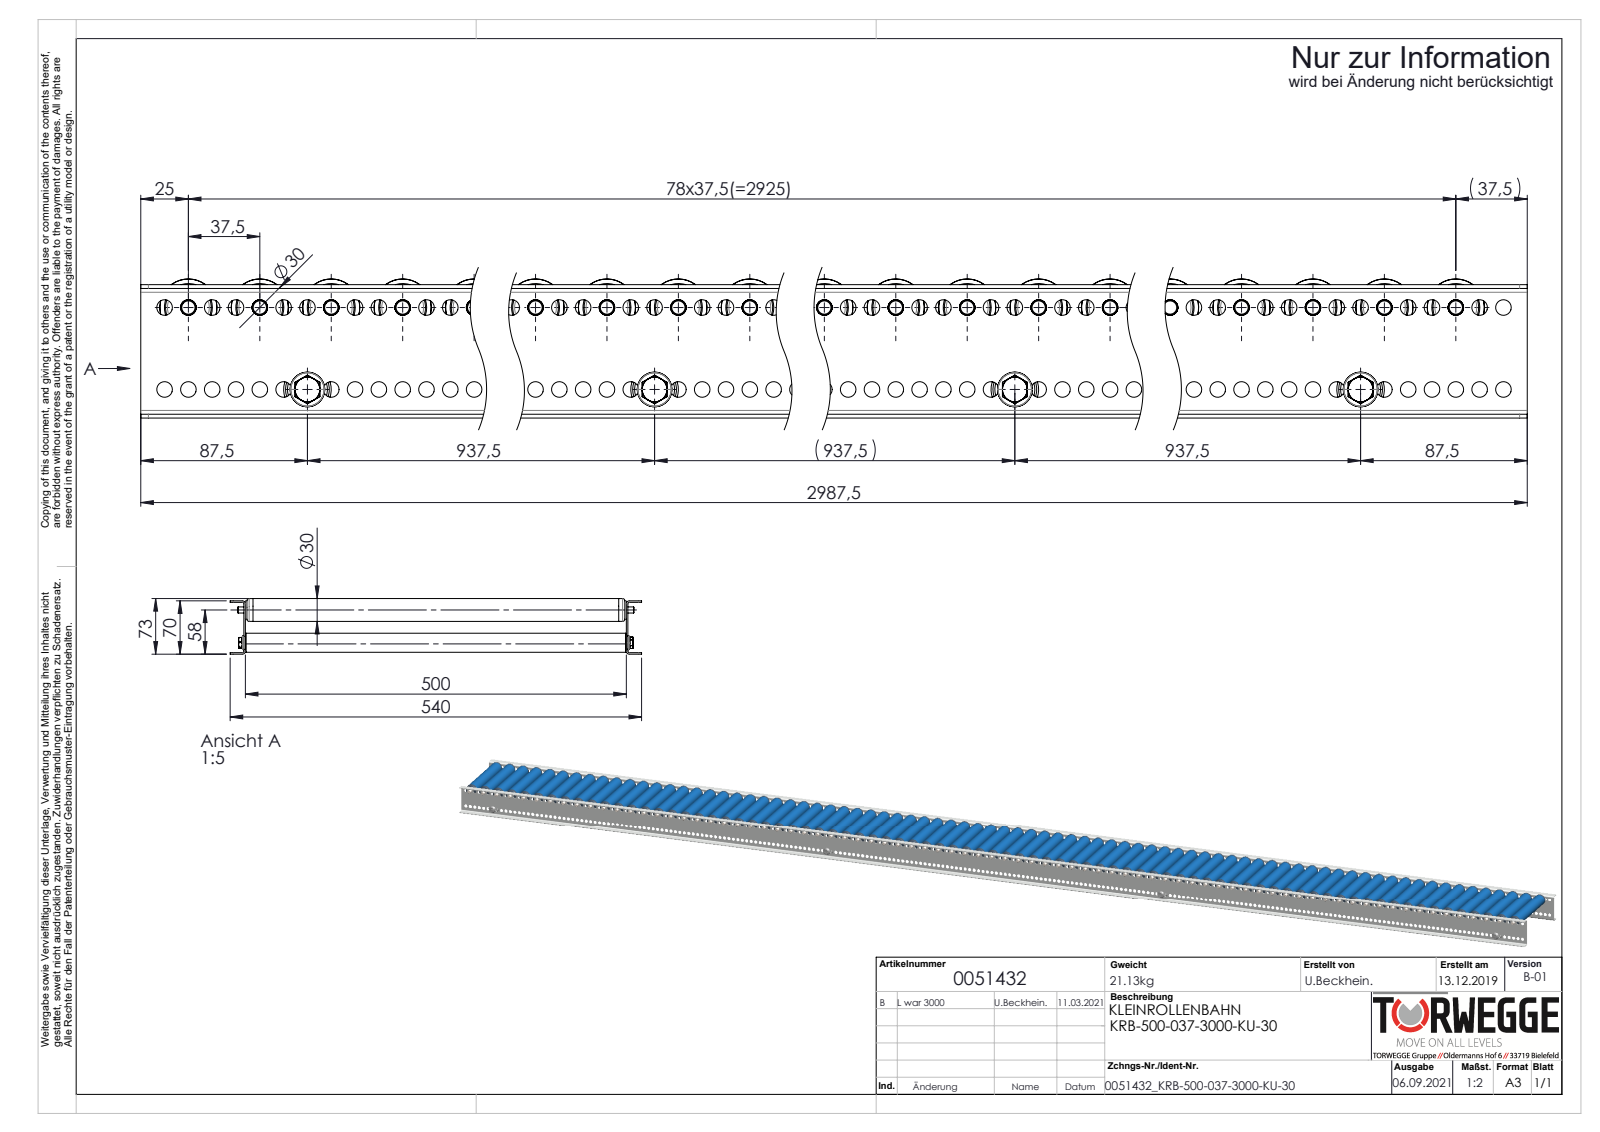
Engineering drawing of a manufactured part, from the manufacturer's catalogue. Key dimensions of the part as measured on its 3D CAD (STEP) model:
Part name (STEP PRODUCT): 0017013_Tragrollenrohr-Ø30x1,8KU_KFG_L=480; Profil_KRB-20x70x20x2_KFG_S109079_U-PROFIL-20-70-20-2-KRB-30-L=2987,5; S100994_Sperrzahnschraube_M08x16-8.8-A2K; Traversen_KFG_L500 (+4 more)
STEP written by: SolidWorks 2020 (AUTOMOTIVE_DESIGN)
Units: millimetres
Bodies: 180 solids, 18686 faces (5734 planar, 7056 cylindrical, 5896 other)
Overall size (bounding box): 2987.5 × 540 × 73
Volume: 9 592 000 mm³ · Surface area: 10 230 000 mm²
Round holes (diameter × count): ⌀8.2 ×476, ⌀8.1 ×79, ⌀22.6 ×79, ⌀25.2 ×79, ⌀6.8 ×4, ⌀21 ×4
Round bosses / shafts (diameter × count): ⌀8 ×83, ⌀30 ×79, ⌀29.9 ×79, ⌀26.5 ×79, ⌀26.4 ×79, ⌀24 ×79, ⌀25 ×4
Partial cylindrical surfaces — rounded edges, fillets, slot ends (radius × count): R5.05 ×79, R4 ×8, R2 ×4
Main face-to-face distances: 2, 502, 68, 500, 504, 70, 66, 10, 490, 12
Hole centre spacings: 12.5, 25, 37.5, 50, 62.5, 75, 87.5, 100
